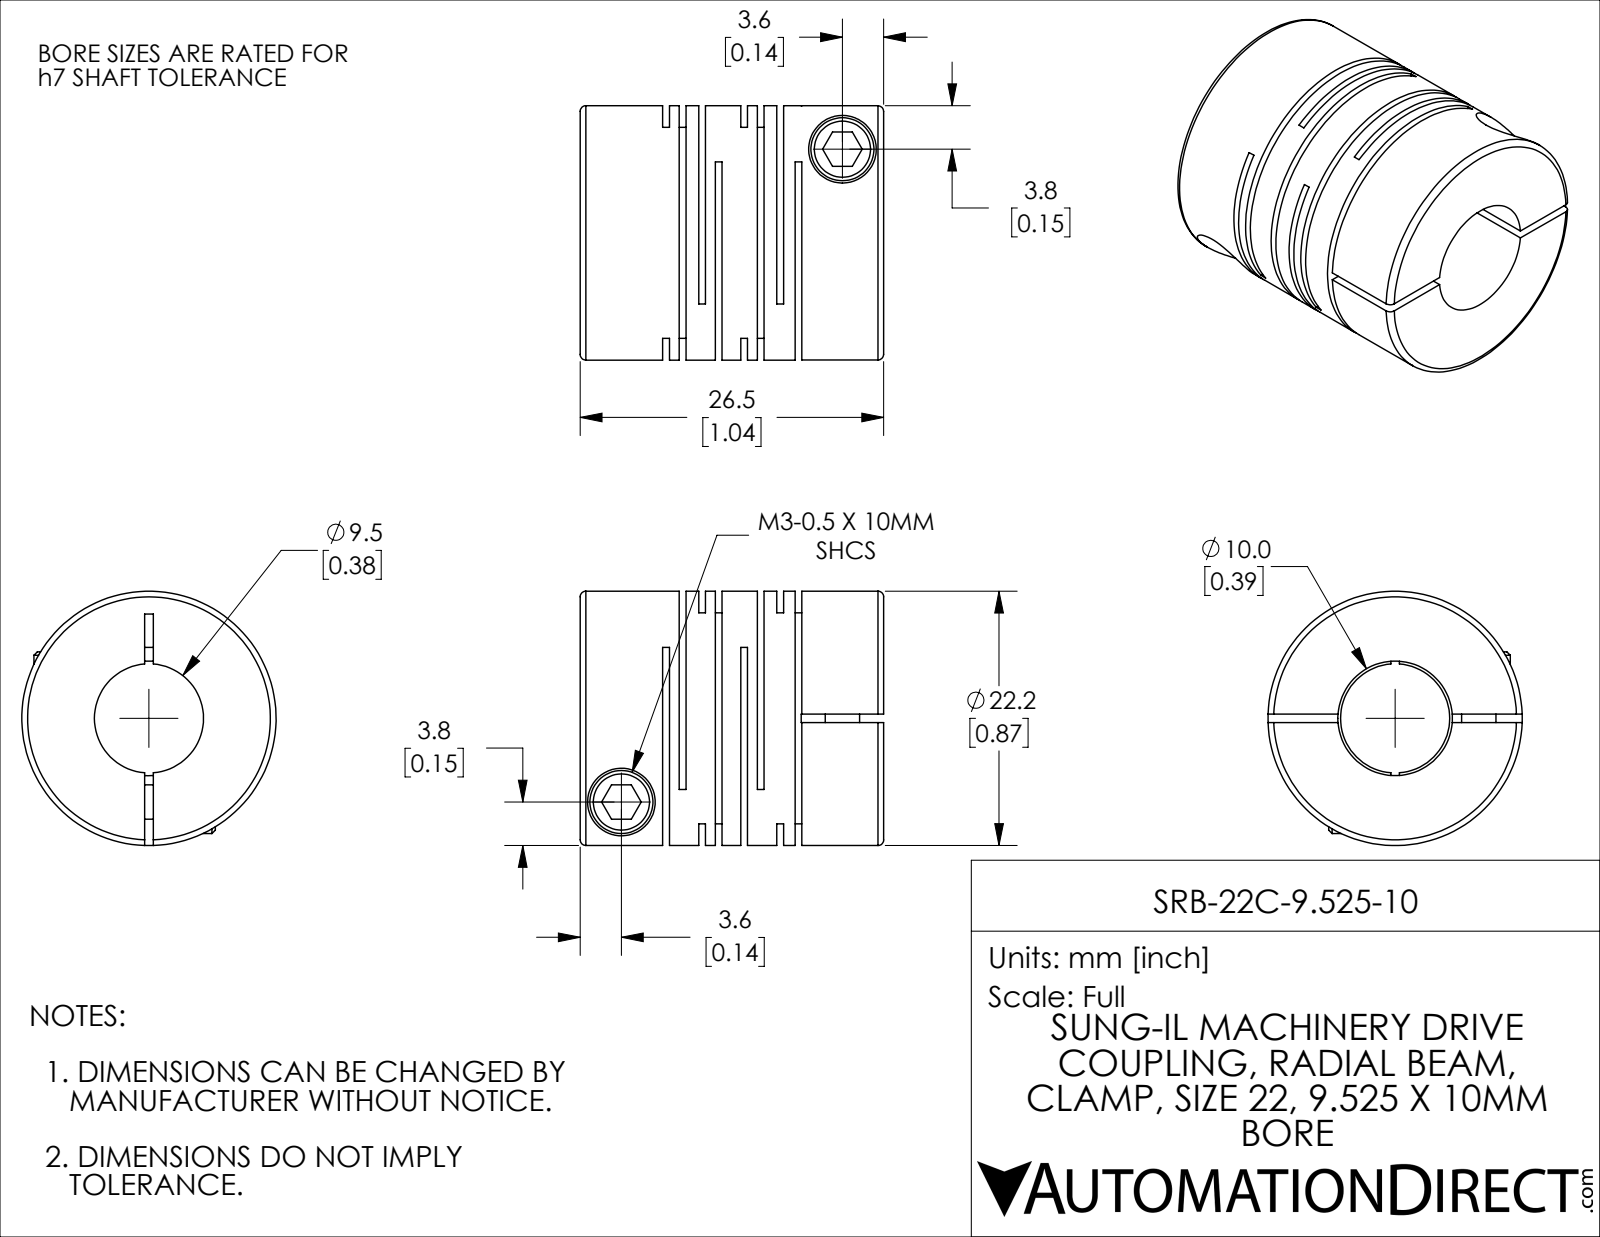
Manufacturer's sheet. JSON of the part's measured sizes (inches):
{"part_name": "SRB-22C-9.525-10", "step_written_by": "SolidWorks 2021 (CONFIG_CONTROL_DESIGN)", "units": "inches", "bodies": {"solids": 1, "faces": 115, "planar": 60, "cylindrical": 42, "other": 13}, "overall_size": [1.043, 0.874, 0.874], "volume_in3": 0.413, "surface_area_in2": 11.54, "round_holes": [[0.118, 2], [0.232, 2], [0.375, 1], [0.394, 1]], "round_bosses_or_shafts": [[0.217, 2], [0.874, 1]], "face_to_face_distances": [0.023, 0.124, 0.269, 0.057, 0.211, 0.144, 0.067, 0.08, 0.147, 0.292]}
